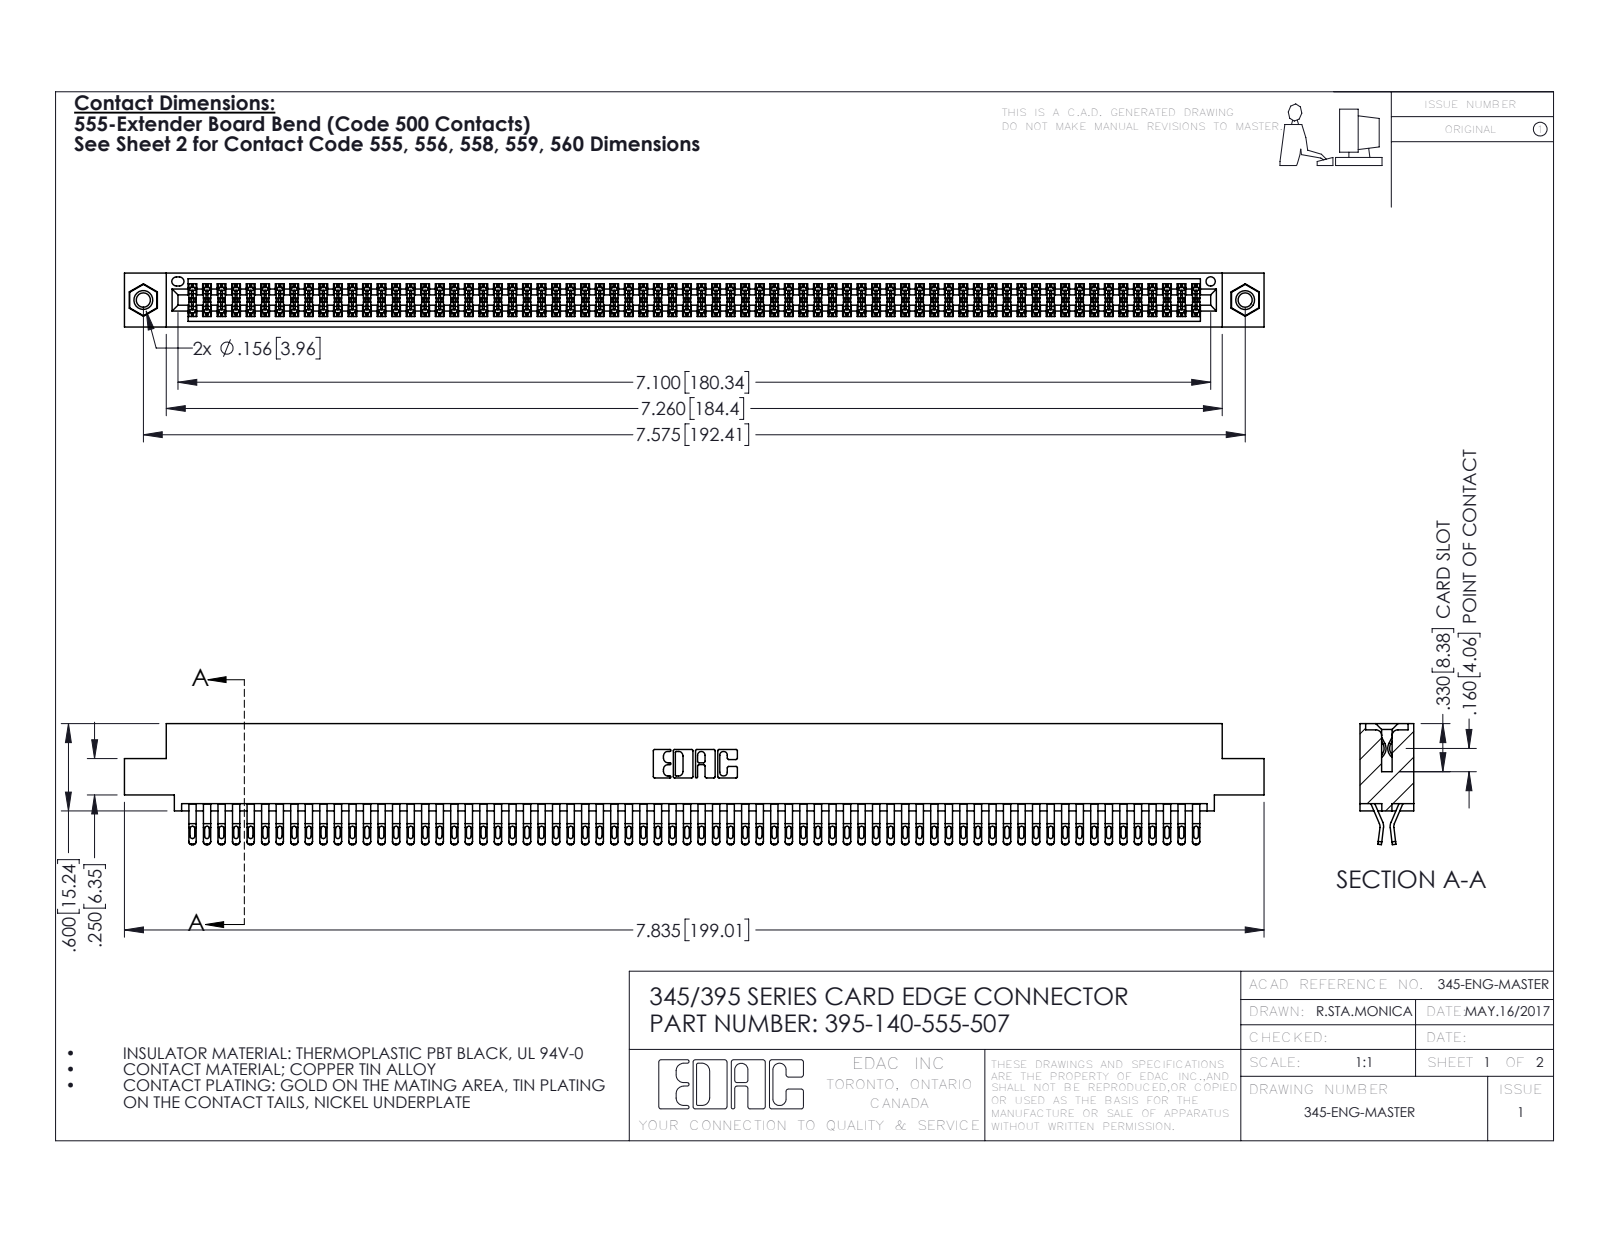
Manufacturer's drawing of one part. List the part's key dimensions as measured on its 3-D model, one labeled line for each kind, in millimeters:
Part name (STEP PRODUCT): 345 Part_0.110 Offset - 0.156 Dia-TI; 345-292-001_555 Tail; 345-250-001_345-250-005-103; 395-140-555-507
STEP written by: SolidWorks 2016 (CONFIG_CONTROL_DESIGN)
Units: millimetres
Bodies: 143 solids, 8030 faces (4456 planar, 3558 cylindrical, 16 other)
Overall size (bounding box): 199 × 21.1 × 9.4
Volume: 19 910 mm³ · Surface area: 31 510 mm²
Round holes (diameter × count): ⌀2.5 ×2, ⌀3.2 ×2, ⌀4 ×2, ⌀1.6 ×1
Round bosses / shafts (diameter × count): ⌀3.9 ×2
Partial cylindrical surfaces — rounded edges, fillets, slot ends (radius × count): R0.4 ×350, R0.5 ×280, R0.2 ×210, R0.3 ×22, R0.2 ×6, R0.8 ×6, R0.7 ×3, R0.3 ×2
Main face-to-face distances: 1.8, 7.6, 0.6, 9.4, 5.1, 2.5, 6.9, 5.7, 4.4, 3.8
Hole centre spacings: 6.9, 186.4, 192.4
